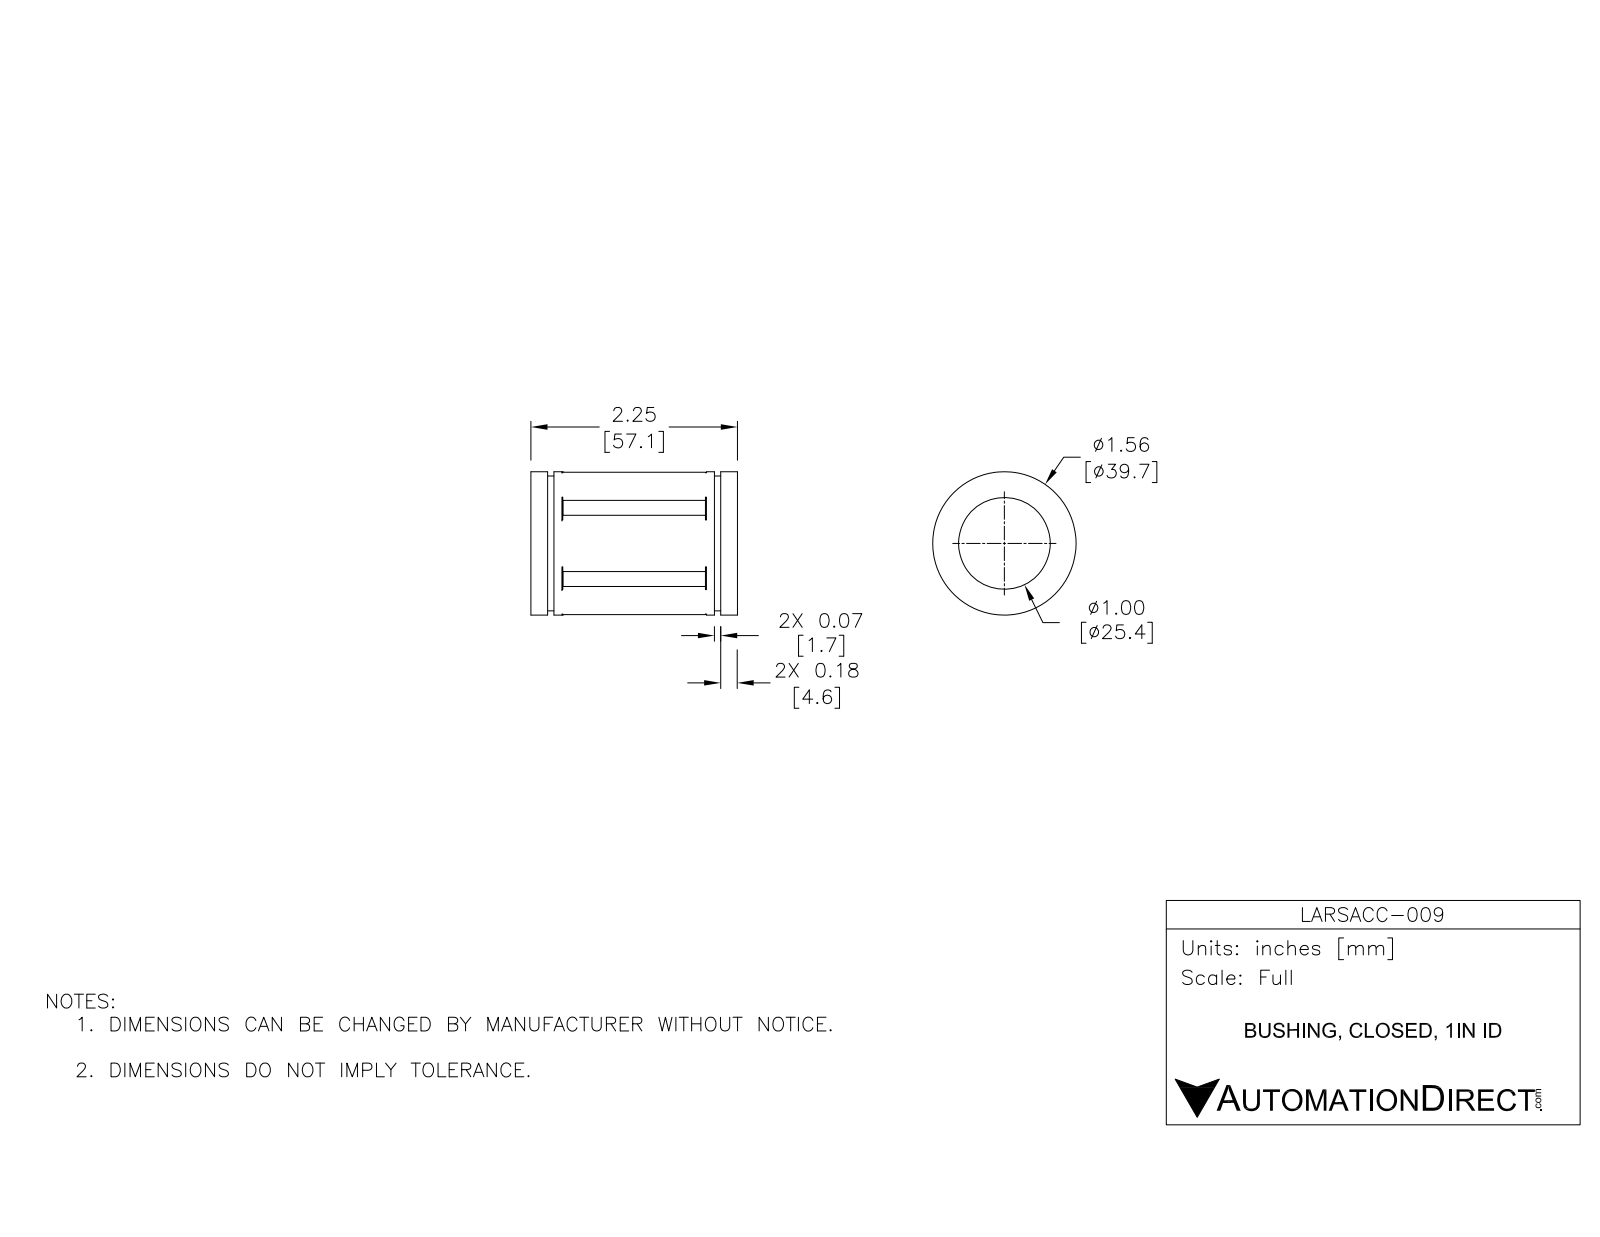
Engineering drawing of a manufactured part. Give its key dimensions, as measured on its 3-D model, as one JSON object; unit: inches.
{"part_name": "LARSACC-009", "step_written_by": "SolidWorks 2015 (AUTOMOTIVE_DESIGN)", "units": "inches", "bodies": {"solids": 1, "faces": 67, "planar": 36, "cylindrical": 31, "other": 0}, "overall_size": [2.25, 1.563, 1.563], "volume_in3": 2.498, "surface_area_in2": 21.38, "round_holes": [[1, 1]], "round_bosses_or_shafts": [[1.563, 1], [1.469, 1]], "partial_cylinders_radius": [[0.453, 6], [0.571, 6]], "face_to_face_distances": [2.25, 0.25, 2, 0.182, 2.068, 0.068, 1.818, 1.75, 1.886, 1.565]}
